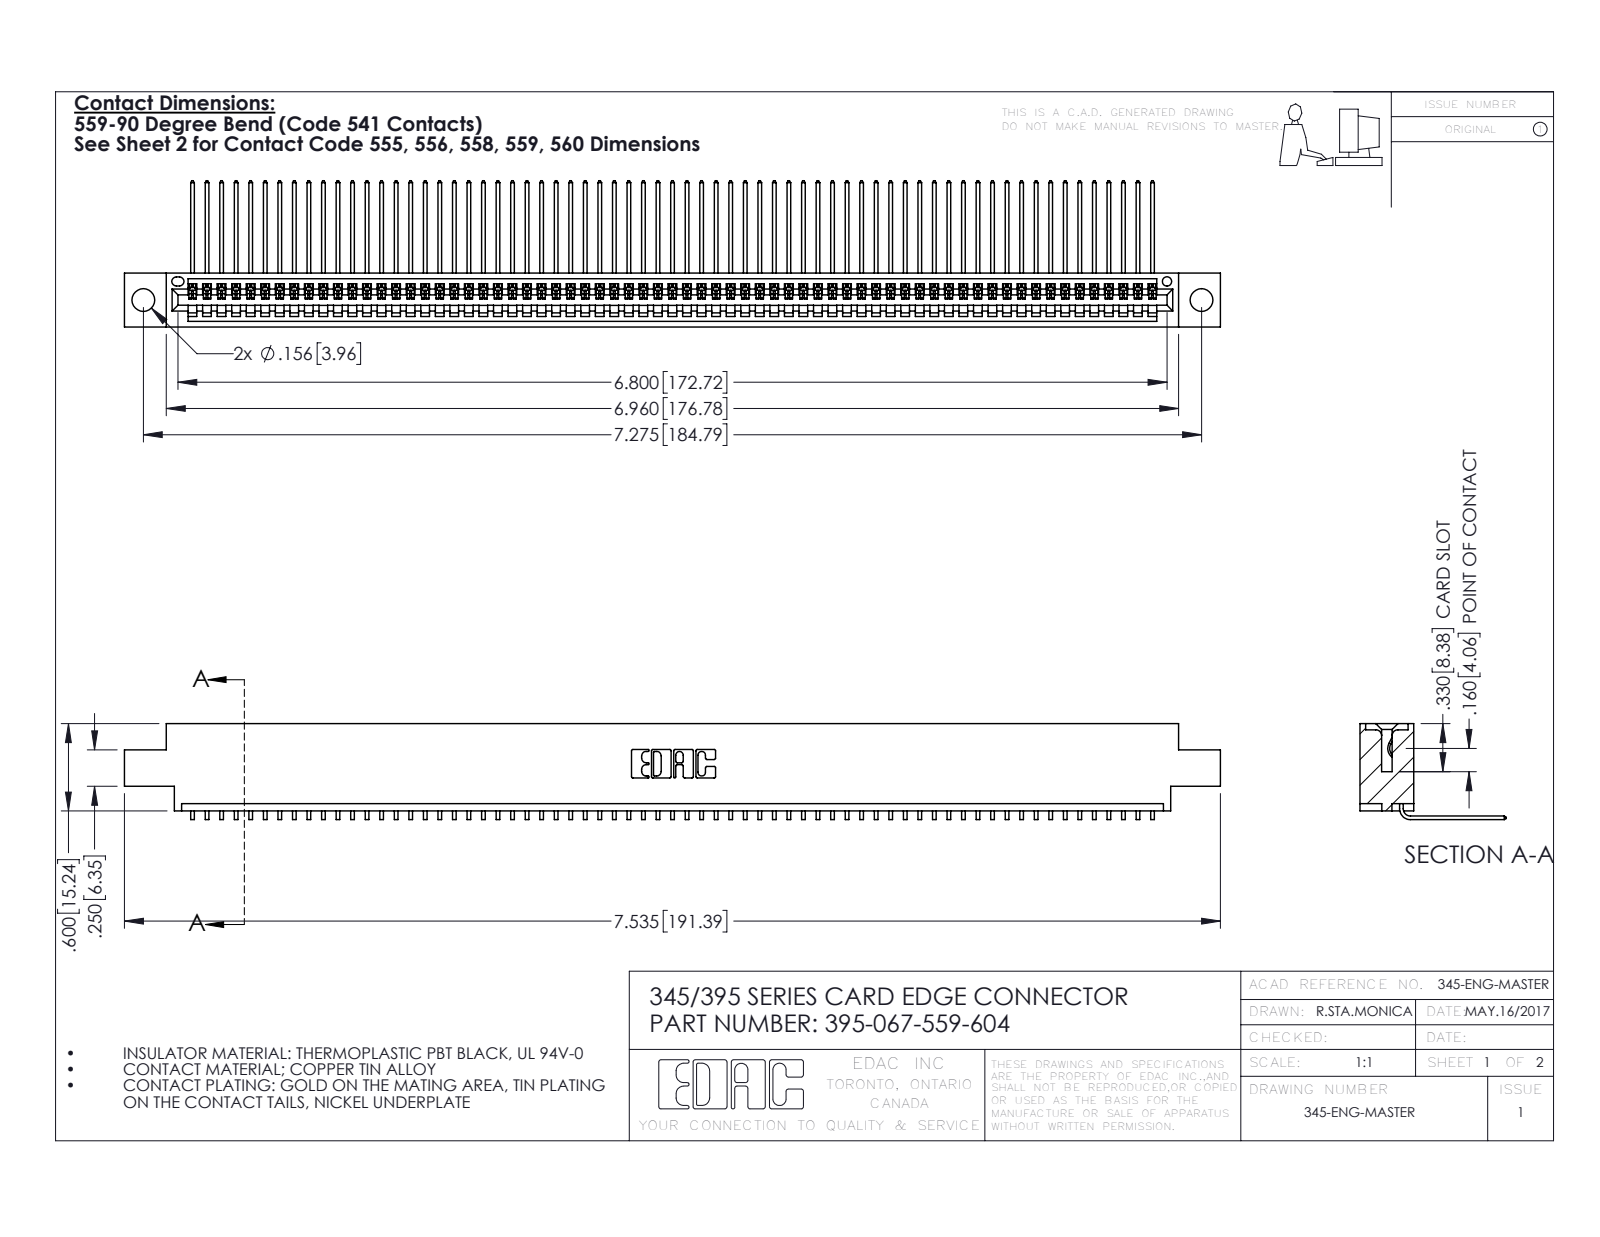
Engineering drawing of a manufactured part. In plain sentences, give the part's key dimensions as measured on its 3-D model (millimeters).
The part is named "395-067-559-604; 345-292-001_558 559 Tail - 1; 345 Part_0.170 Offset - 0.156 Dia-TH". Its 3-D file was written by "SolidWorks 2016 (CONFIG_CONTROL_DESIGN)". It is 68 solids with 4150 faces: 2898 planar, 1252 cylindrical and 0 other. Overall it measures 191.4 by 25.5 by 16.7 millimeters. Its volume is 18 400 cubic millimeters and its surface area 26 050 square millimeters. Round holes: 2 of diameter 4, 1 of diameter 1.6. Partial cylindrical surfaces (rounded edges, fillets, slot ends): 134 of radius 0.2, 22 of radius 0.3, 6 of radius 0.2, 6 of radius 0.8, 3 of radius 0.7, 2 of radius 0.8, 2 of radius 1, 1 of radius 0.4. The main face-to-face distances are 1.8, 7.6, 9.4, 5.1, 2.5, 6.9, 0.6, 5.7, 4.4, 3.8. The hole center spacings are 6.9, 178.8, 184.8.
